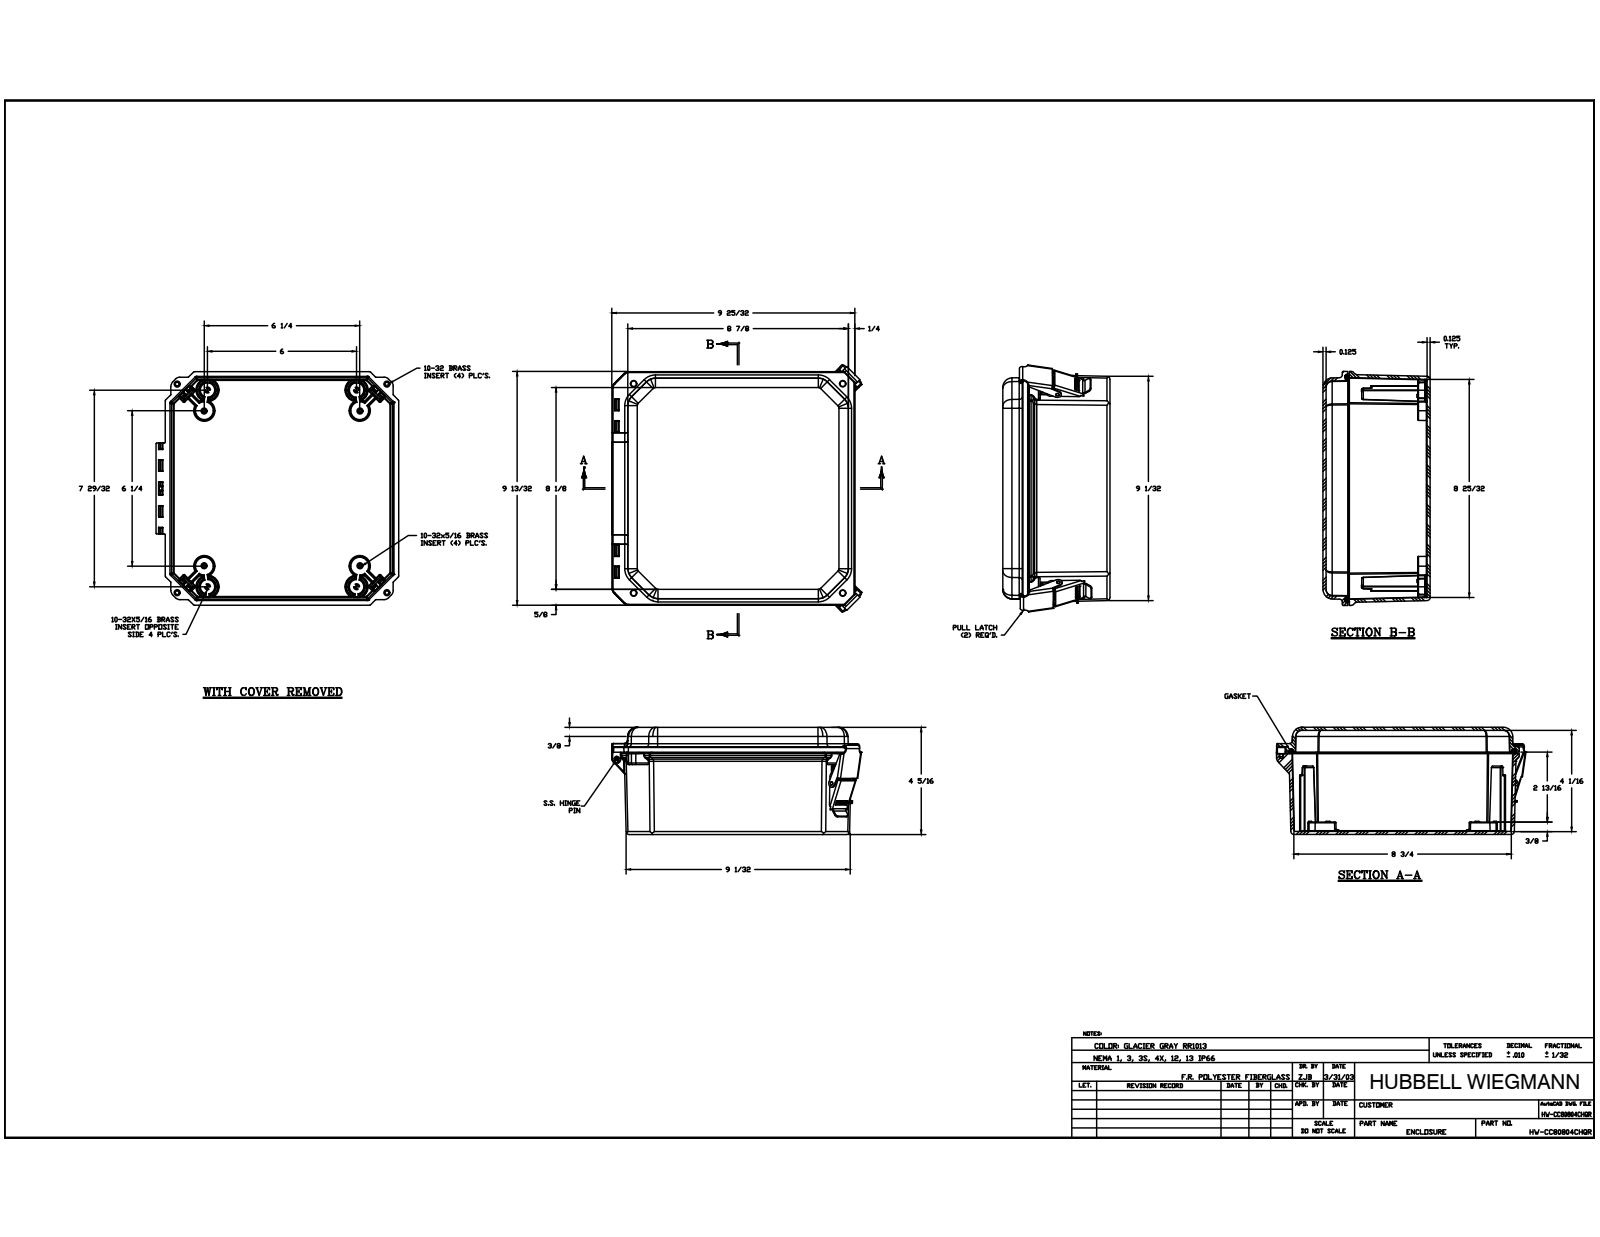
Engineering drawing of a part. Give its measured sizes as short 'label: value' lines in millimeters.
name: DS080804BOX; DSCC080804CVR; GA808; WP808HLU (+6 more)
written by: Autodesk Inventor 2014 (AUTOMOTIVE_DESIGN)
unit: mm
bodies: 29 solids, 2157 faces (646 planar, 841 cylindrical, 670 other)
size: 256.43 × 255.16 × 109.53
volume: 740 265 mm³; area: 459 520 mm²
holes: 12× ⌀3.96, 9× ⌀3.43, 8× ⌀3.86, 4× ⌀3.81, 4× ⌀5.56, 4× ⌀6.4, 4× ⌀7.92, 2× ⌀3.43, 2× ⌀9.52, 1× ⌀3.48
bosses: 12× ⌀6.25, 4× ⌀22.1, 4× ⌀7.62, 4× ⌀5.3, 3× ⌀3.43
rounds: 140× R0.25, 94× R0.13, 67× R0.51, 58× R0.76, 29× R3.17, 26× R2.29, 24× R0.76, 24× R1.52
face distances: 3.17, 106.35, 109.52, 103.18, 3.15, 89.69, 16.66, 22.23, 25.4, 84.12
hole spacings: 6.35, 158.75, 158.76, 188.25, 21.27, 156.99, 179.82, 188.23
